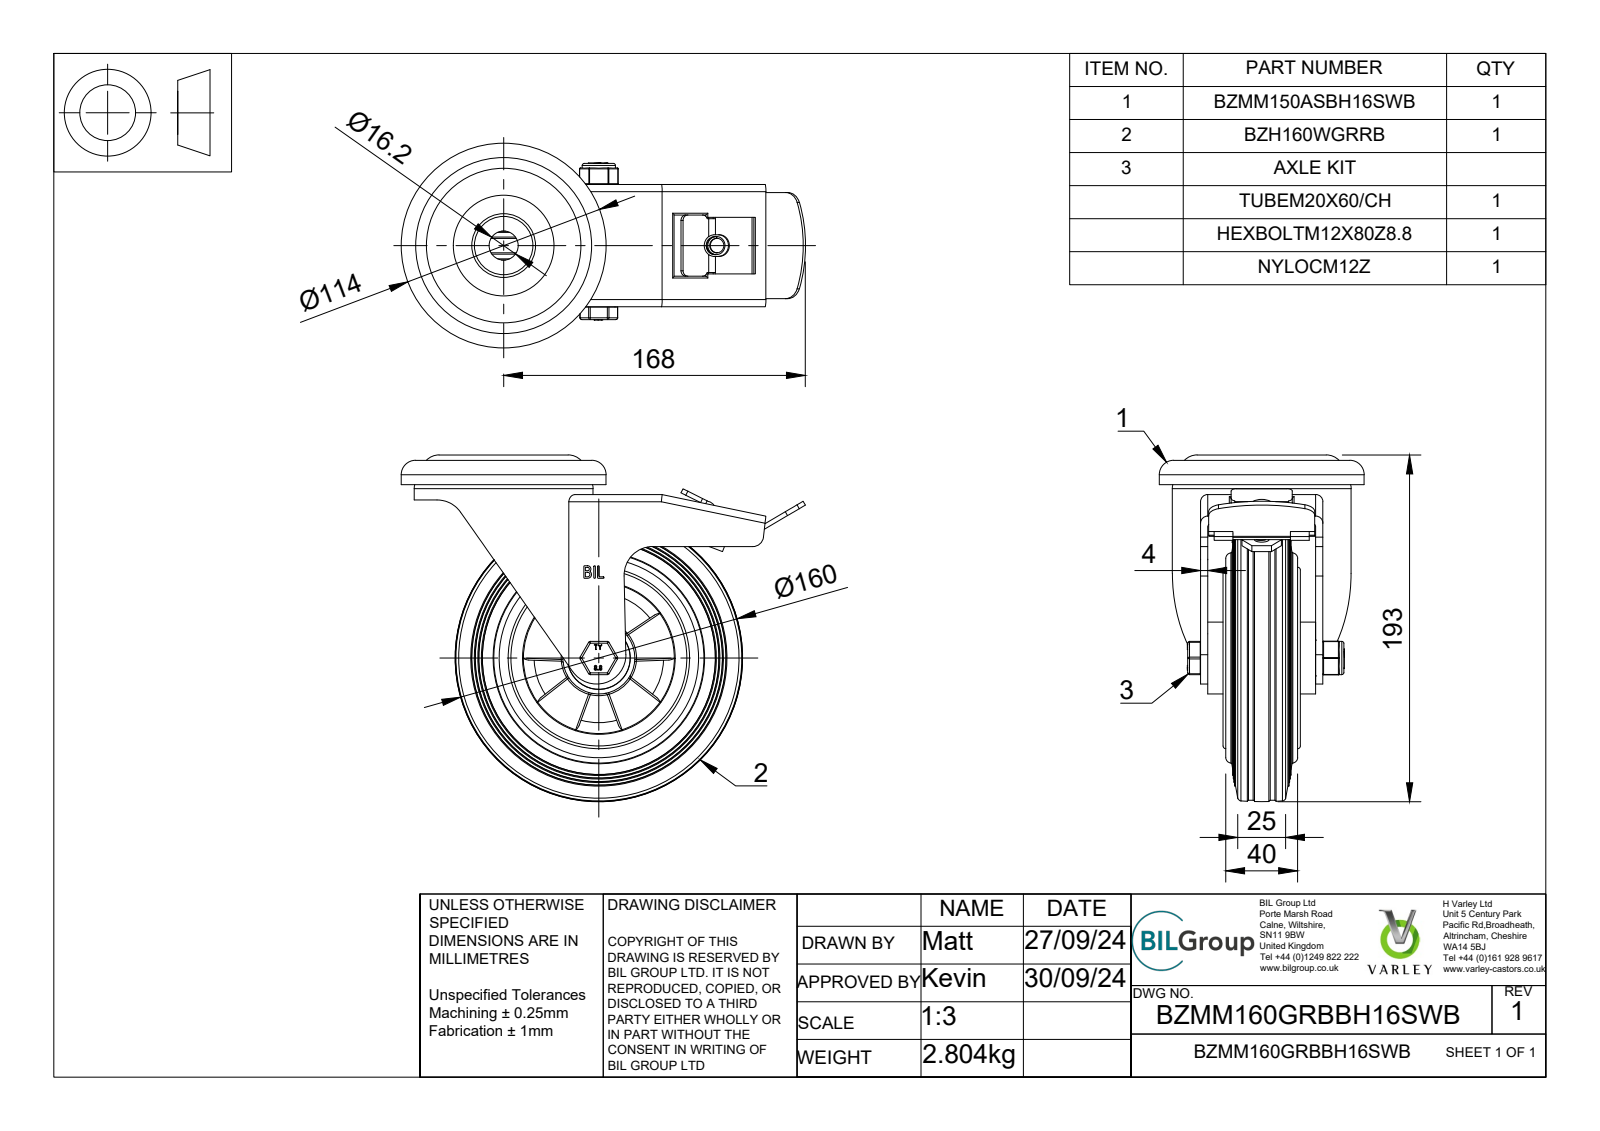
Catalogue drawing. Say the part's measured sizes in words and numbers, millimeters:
The part is named "BZMM160GRBBH16SWB v3; BZMM150ASBH16SWB v1; ZINC PLATED, PRESSED STEEL HEAD; ZINC PLATED, PRESSED STEEL FORKS (+8 more)". Its 3-D file was written by "Autodesk Translation Framework v13.20.0.188 (AUTOMOTIVE_DESIGN)". It is 22 solids with 887 faces: 347 planar, 211 cylindrical and 329 other. Overall it measures 225 by 193 by 114 millimeters. Its volume is 838 972 cubic millimeters and its surface area 277 434 square millimeters. Round holes: 1 of diameter 10, 1 of diameter 10.27, 1 of diameter 12, 1 of diameter 12.2, 1 of diameter 12.5, 1 of diameter 14, 1 of diameter 16.2, 1 of diameter 20, 1 of diameter 34, 1 of diameter 35, 1 of diameter 41, 1 of diameter 51.5. Round bosses or shafts: 8 of diameter 7.5, 1 of diameter 158.4, 1 of diameter 114, 1 of diameter 101, 1 of diameter 99.5, 1 of diameter 74, 1 of diameter 47, 1 of diameter 40. Partial cylindrical surfaces (rounded edges, fillets, slot ends): 22 of radius 0.5, 18 of radius 1, 8 of radius 2, 4 of radius 3, 4 of radius 4, 3 of radius 6, 3 of radius 8, 2 of radius 16. The main face-to-face distances are 4, 1, 8.5, 2.5, 5.75, 3, 7.75, 60, 17.25, 64.
